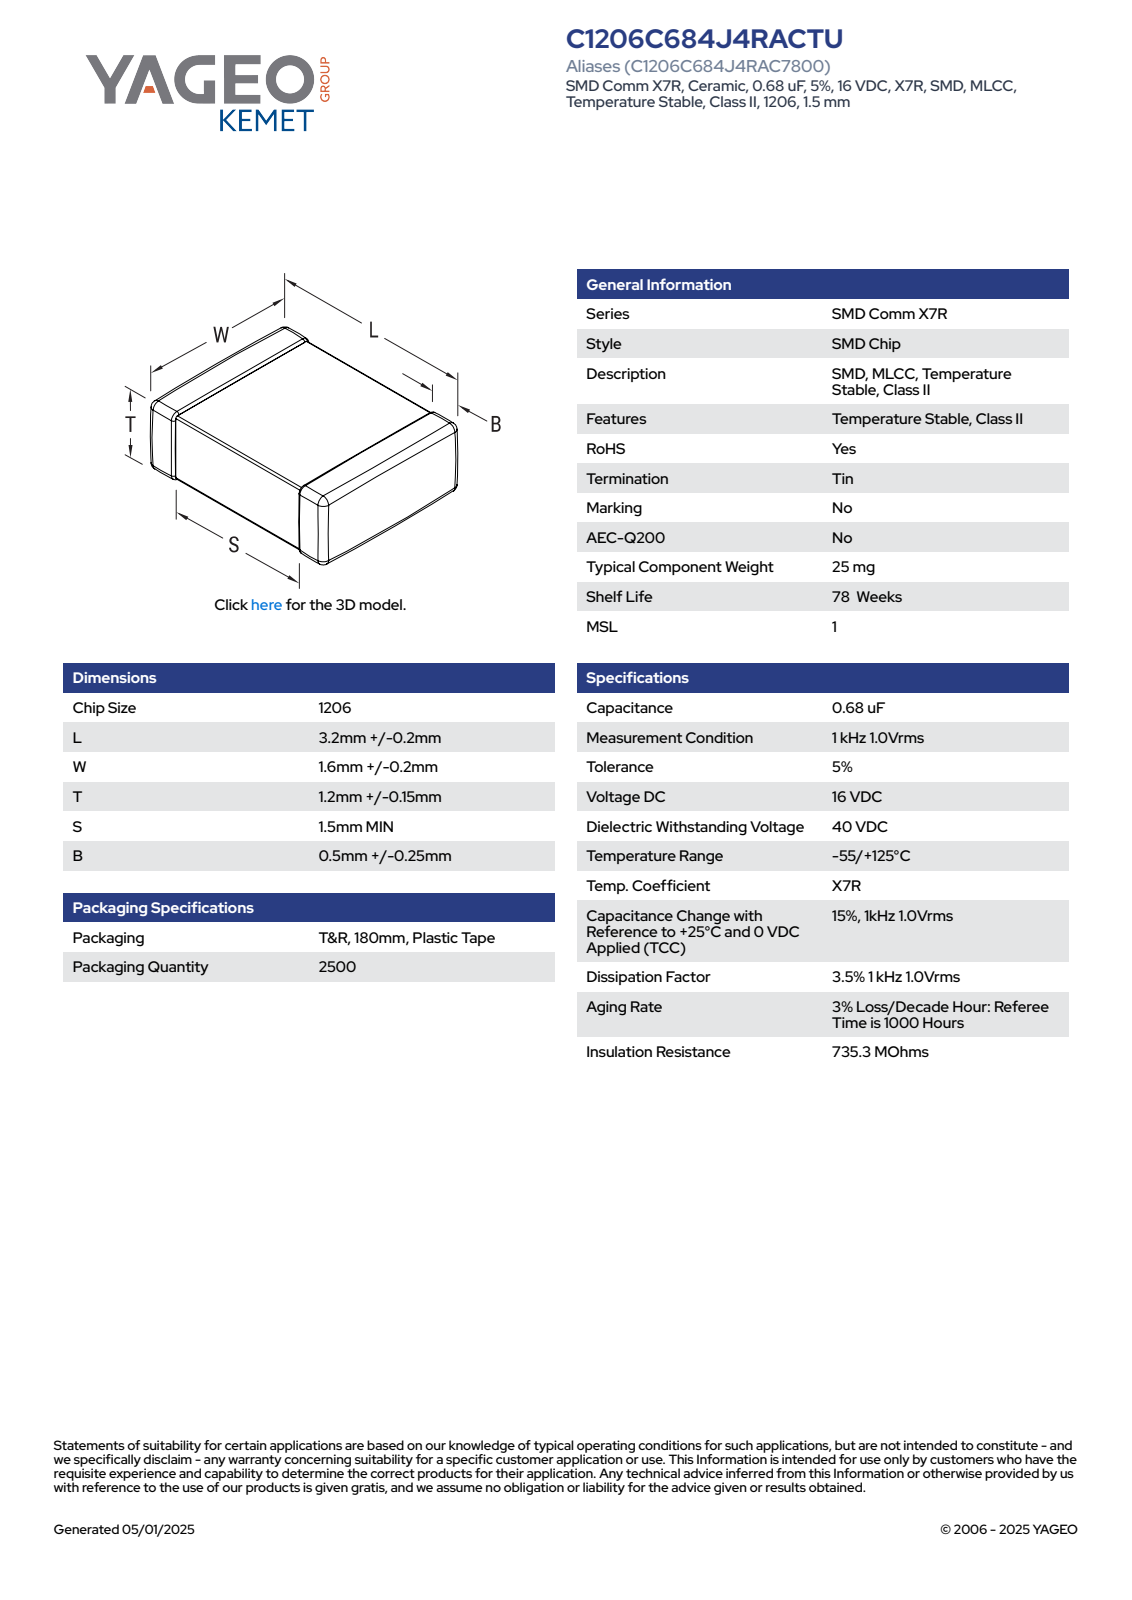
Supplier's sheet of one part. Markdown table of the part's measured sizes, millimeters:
| quantity | value |
| --- | --- |
| part name | CCS_CCSTD_1206_L3.4W1.8T1.35B0.5 |
| STEP written by | SolidWorks 2021 (AUTOMOTIVE_DESIGN) |
| units | millimeters |
| bodies | 4 solids, 125 faces (71 planar, 38 cylindrical, 16 other) |
| overall size | 3.4 × 1.8 × 1.35 |
| volume | 8 mm³ |
| surface area | 26 mm² |
| main face-to-face distances | 1.31, 1.76, 1.27, 1.35, 1.72, 3.4, 1.8, 1.32, 1.28, 1.57 |
